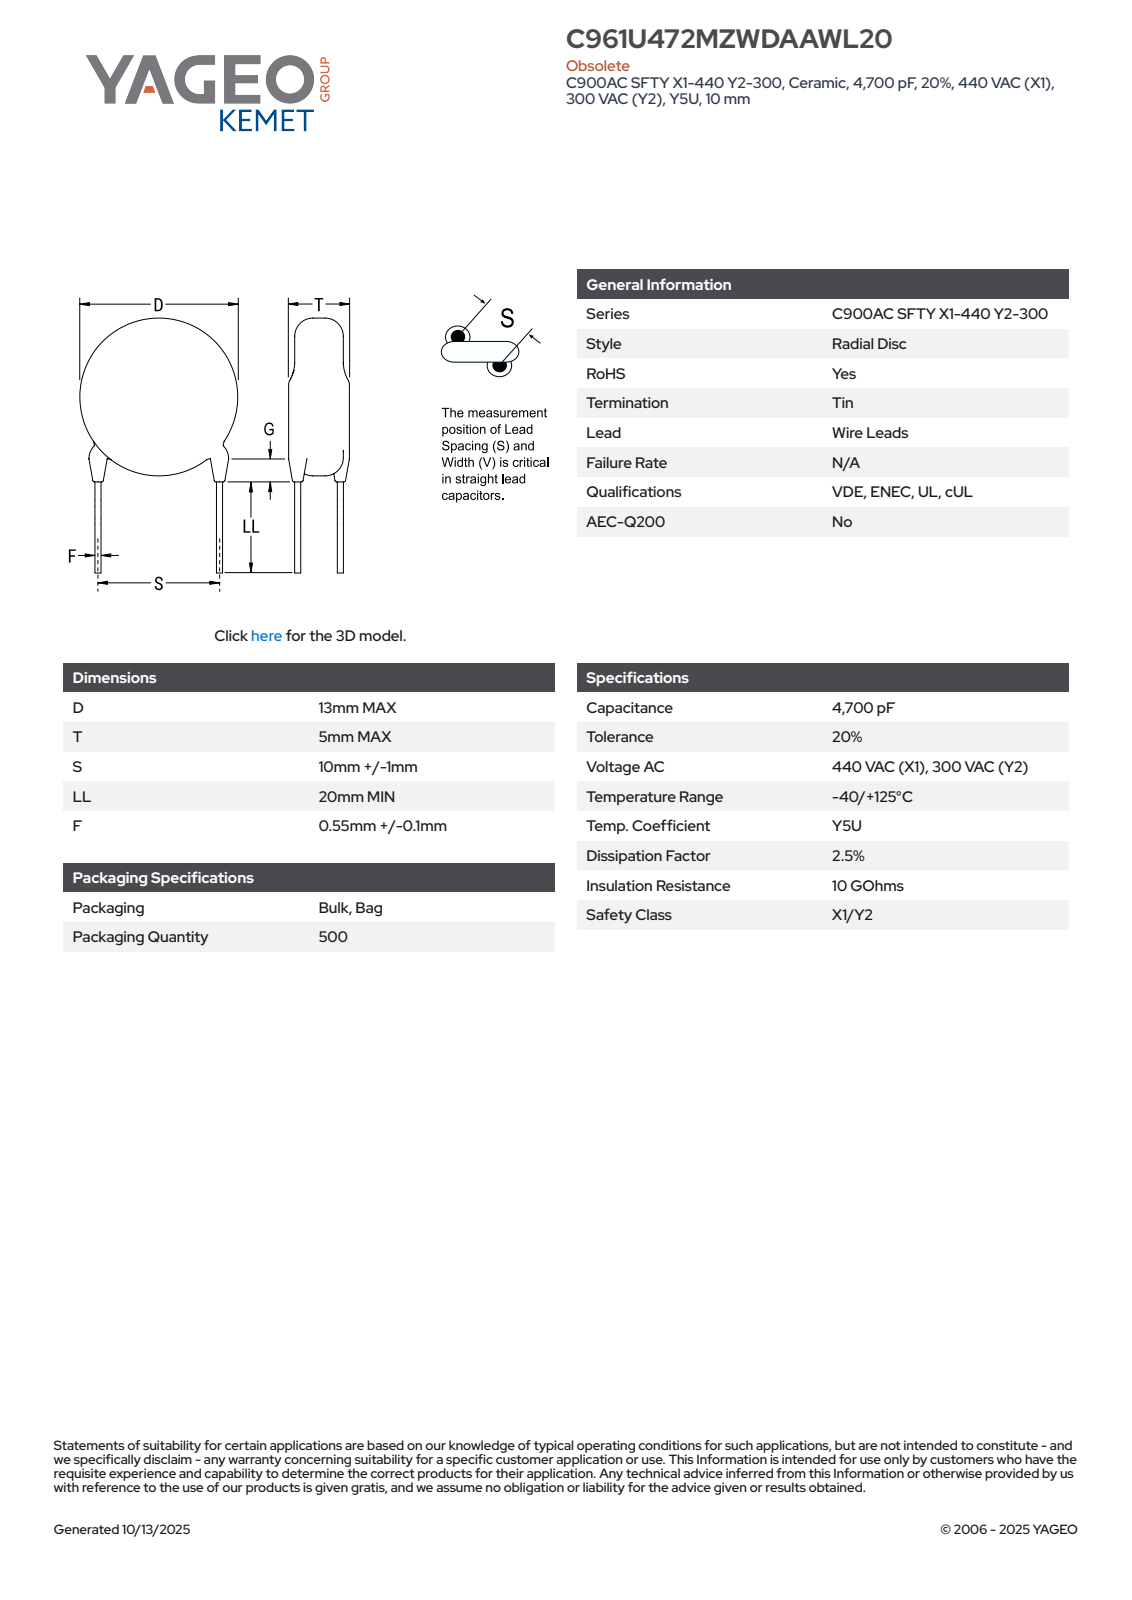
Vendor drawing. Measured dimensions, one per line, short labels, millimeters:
name: CCD_STC900_D13T5S10LL20F0.65G3
written by: SolidWorks 2014 (AUTOMOTIVE_DESIGN)
unit: mm
bodies: 4 solids, 83 faces (61 planar, 6 cylindrical, 16 other)
size: 33.31 × 13 × 5
volume: 663 mm³; area: 540 mm²
bosses: 2× ⌀0.65, 1× ⌀13
face distances: 5, 1.5, 27.56, 26.06, 0.41, 6.13, 0.93, 3.1, 4.45, 4.63
